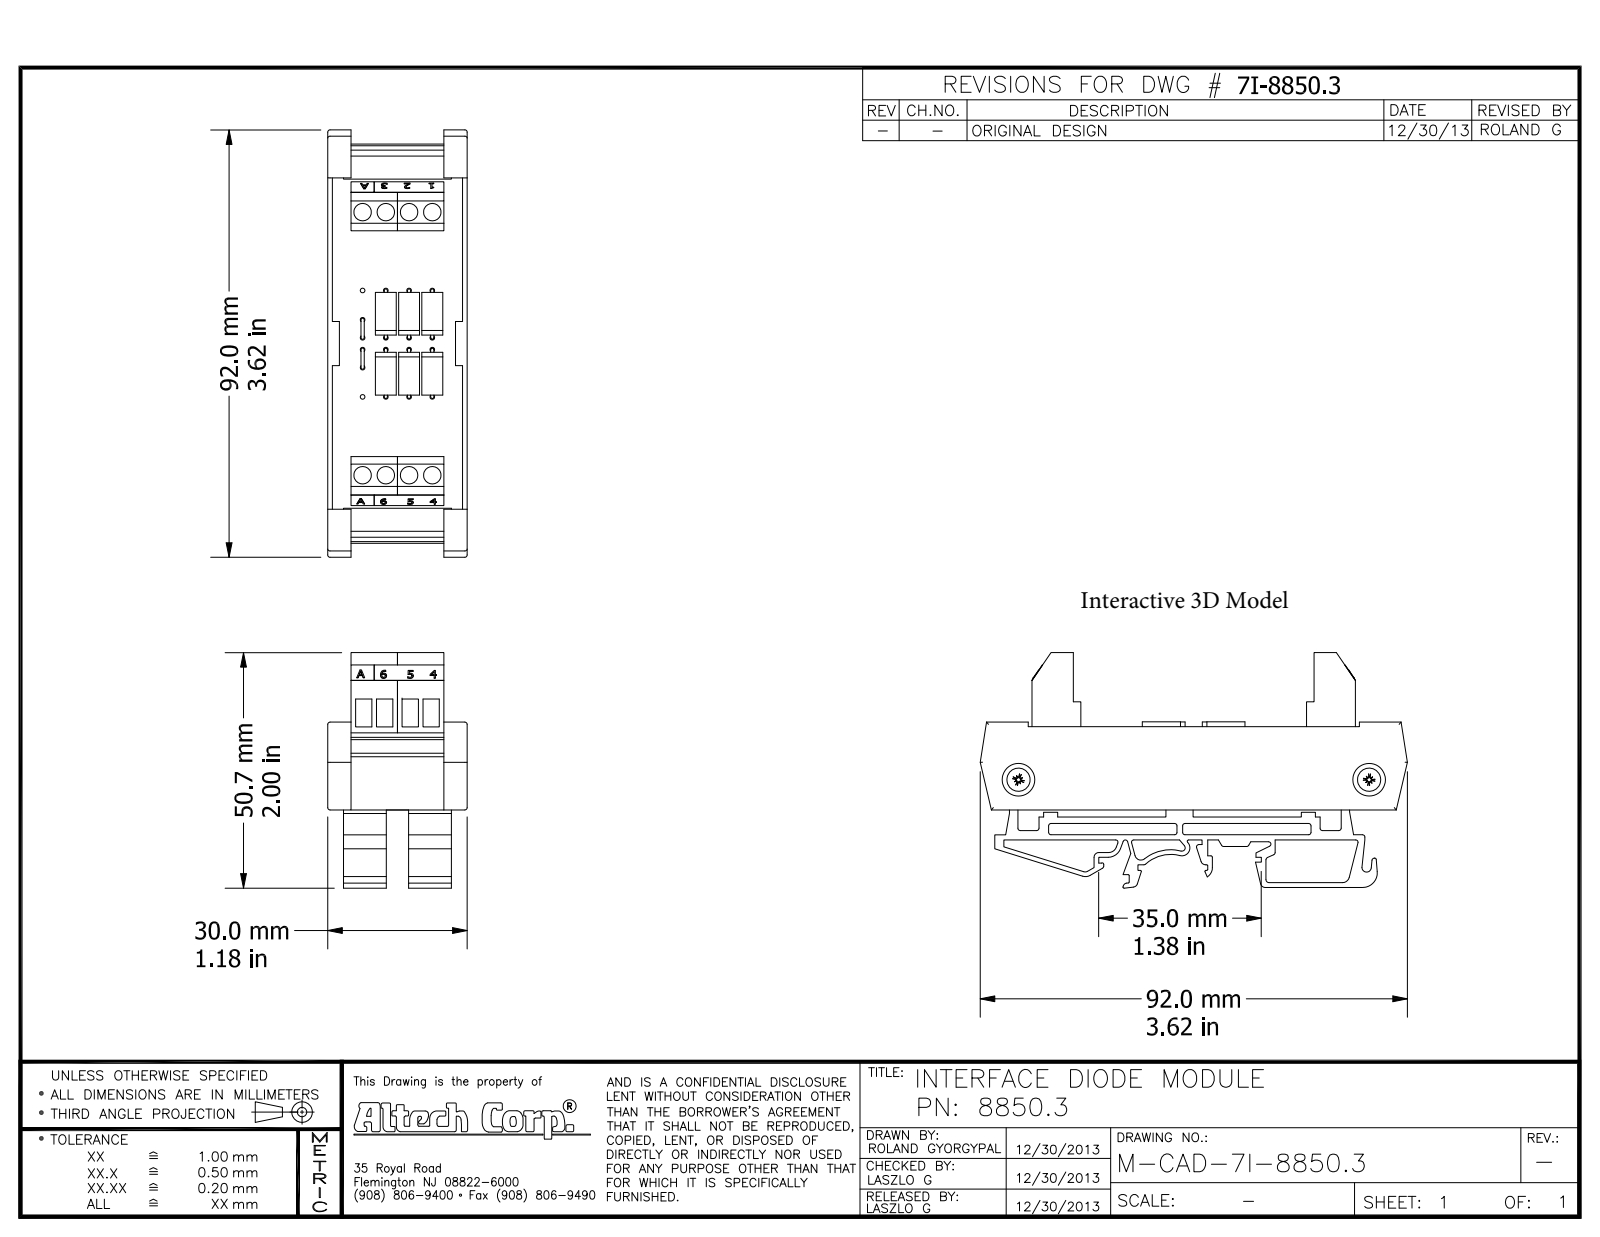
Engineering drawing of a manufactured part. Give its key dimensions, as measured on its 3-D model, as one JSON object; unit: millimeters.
{"part_name": "8850; 6 plate; 2 hole green; bussed filler (+8 more)", "step_written_by": "Autodesk Inventor 2013 (CONFIG_CONTROL_DESIGN)", "units": "millimeters", "bodies": {"solids": 26, "faces": 1267, "planar": 775, "cylindrical": 313, "other": 179}, "overall_size": [91.98, 50.69, 30], "volume_mm3": 28183, "surface_area_mm2": 41841, "round_holes": [[1, 24], [1.3, 8], [3.75, 8], [0.68, 5], [3.2, 2], [7, 2]], "round_bosses_or_shafts": [[0.68, 15], [0.69, 6], [4.5, 3], [4.49, 3], [9, 2], [2.5, 2], [2.26, 2]], "partial_cylinders_radius": [[0.5, 25], [0.51, 16], [0.5, 15], [0.3, 11], [0.2, 9], [0.3, 4], [0.41, 4], [0.81, 4]], "face_to_face_distances": [1, 2.4, 14, 29, 11.6, 13.85, 13.35, 0.5, 26.6, 15], "hole_center_spacings": [5, 10, 8.04, 17.34, 27.49, 30, 6.3, 11.82]}
